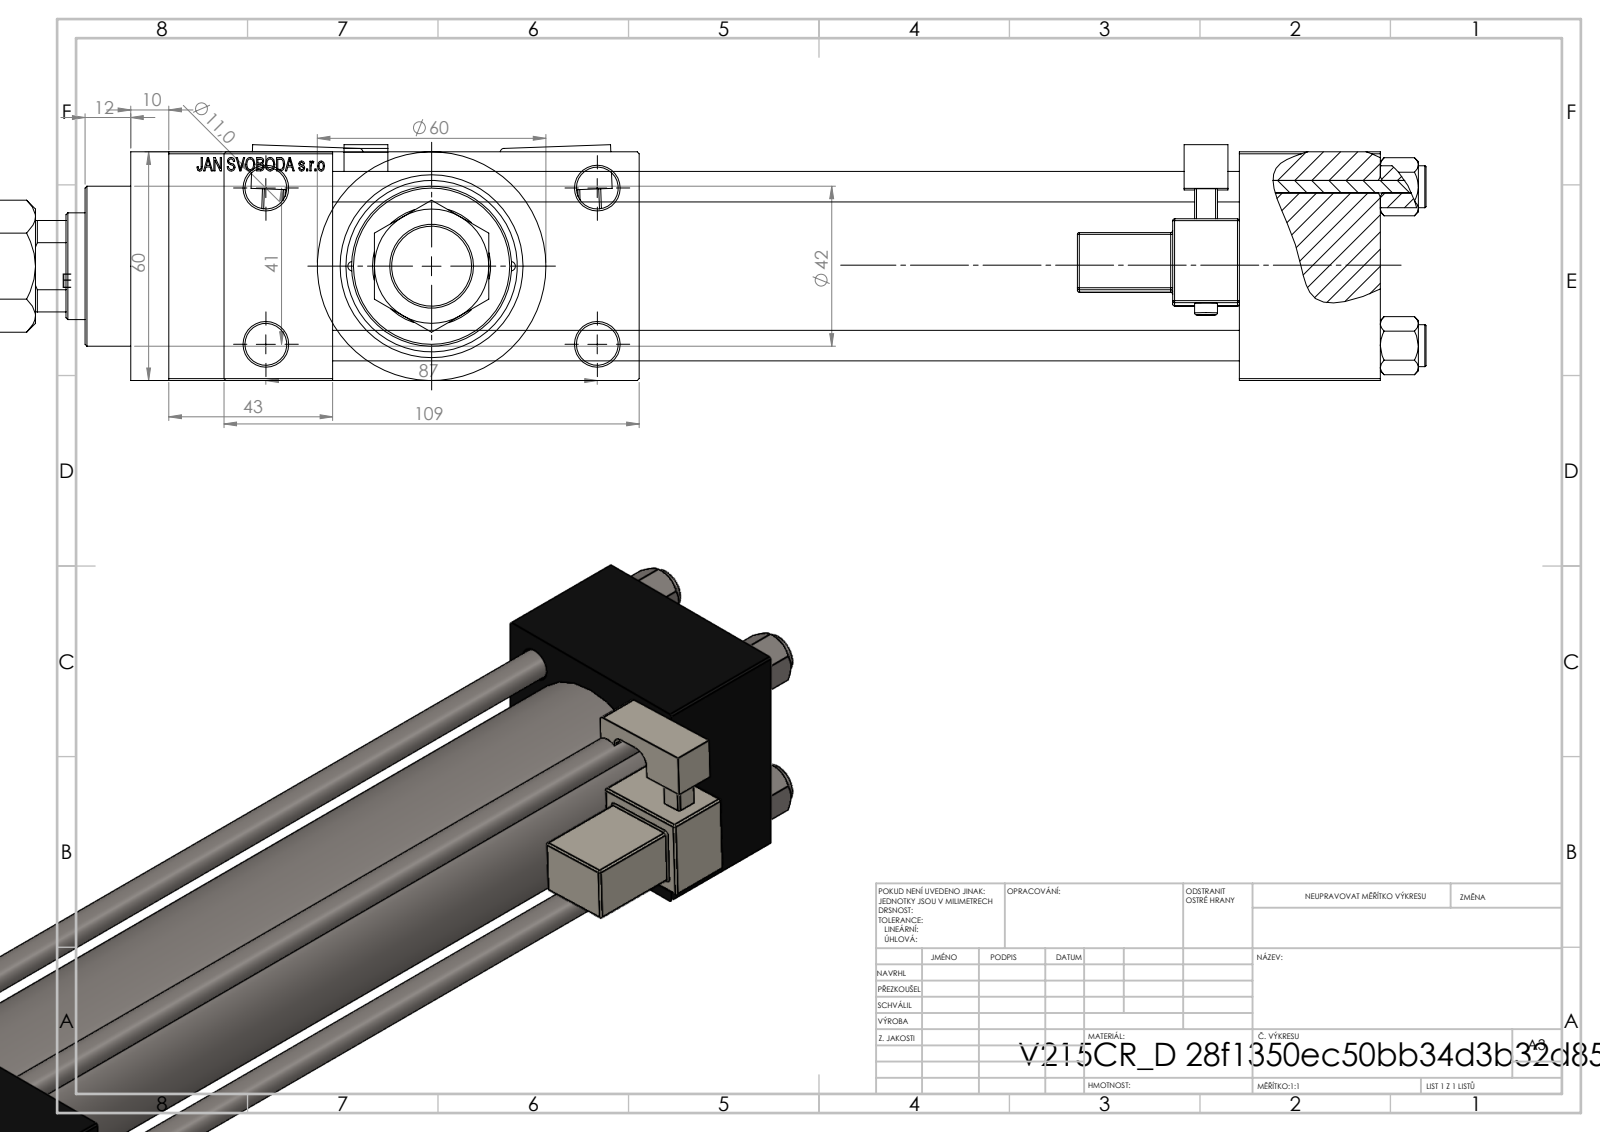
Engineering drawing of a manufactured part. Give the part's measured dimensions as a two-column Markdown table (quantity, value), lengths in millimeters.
| quantity | value |
| --- | --- |
| part name | V215CR_D_TYCINKA; V215CR_D_Body; V215CR_MSU; NUT_M5_D (+3 more) |
| STEP written by | SolidWorks 2019 (CONFIG_CONTROL_DESIGN) |
| units | millimeters |
| bodies | 14 solids, 1320 faces (576 planar, 156 cylindrical, 588 other) |
| overall size | 410 × 109 × 61.9 |
| volume | 814 110 mm³ |
| surface area | 229 314 mm² |
| round holes (diameter × count) | 8 × 4, 11 × 4, 2.5 × 2, 7 × 2, 16.66 × 2, 24 × 2, 18.5 × 1, 28 × 1, 31 × 1, 40 × 1, 45 × 1 |
| round bosses / shafts (diameter × count) | 11 × 4, 6 × 2, 60 × 1, 46 × 1, 42 × 1, 22 × 1, 14 × 1 |
| partial cylindrical surfaces (radius × count) | 0.5 × 48, 1 × 2, 2.5 × 2, 4 × 2, 13.5 × 1 |
| main face-to-face distances | 60, 238, 24.5, 84.5, 37, 275, 318, 281, 43, 109 |
| hole center spacings | 20.85, 22.65, 29.49, 30.62, 41.7, 46.53, 47.15, 48.09 |
